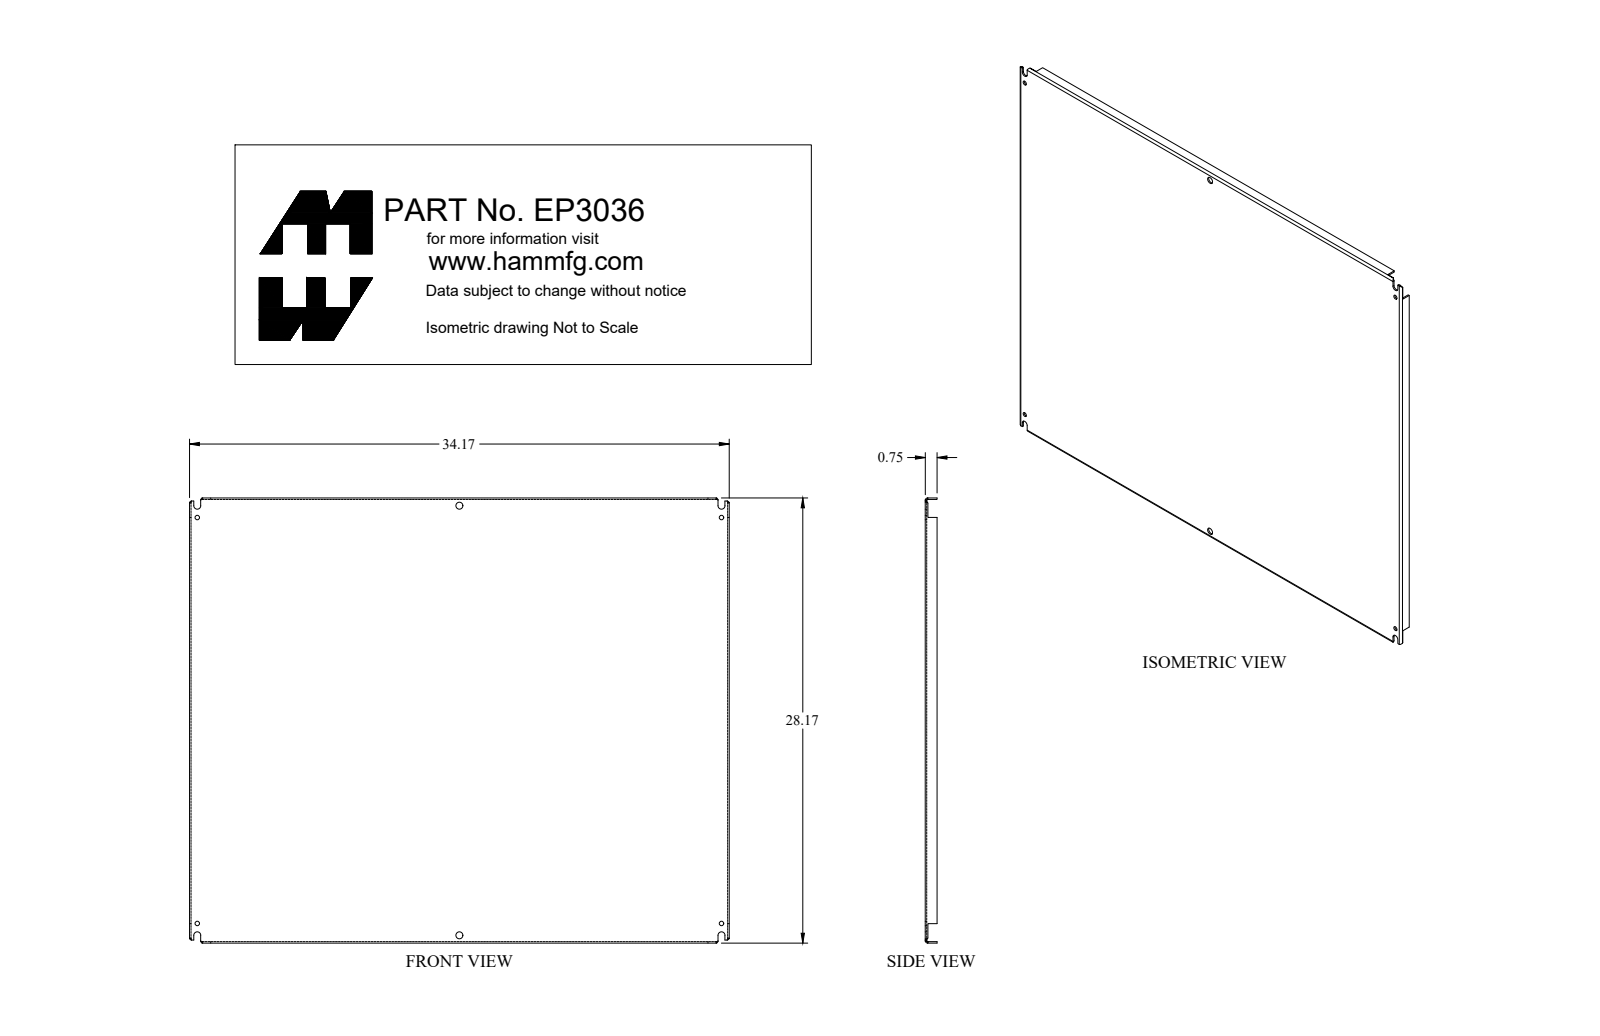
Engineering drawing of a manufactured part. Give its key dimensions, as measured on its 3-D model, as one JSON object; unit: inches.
{"part_name": "EP3036", "step_written_by": "SolidWorks 2018 (AUTOMOTIVE_DESIGN)", "units": "inches", "bodies": {"solids": 1, "faces": 132, "planar": 74, "cylindrical": 42, "other": 16}, "overall_size": [34.17, 28.17, 0.75], "volume_in3": 97.94, "surface_area_in2": 2075, "round_holes": [[0.281, 4], [0.437, 2]], "partial_cylinders_radius": [[0.048, 4], [0.063, 4], [0.143, 4], [0.219, 4]], "face_to_face_distances": [0.095, 28.075, 34.075, 27.98, 28.17, 33.98, 34.17, 0.75, 0.655, 0.171], "hole_center_spacings": [16.611, 31.215, 25.688, 33.188, 41.969, 27.188]}
